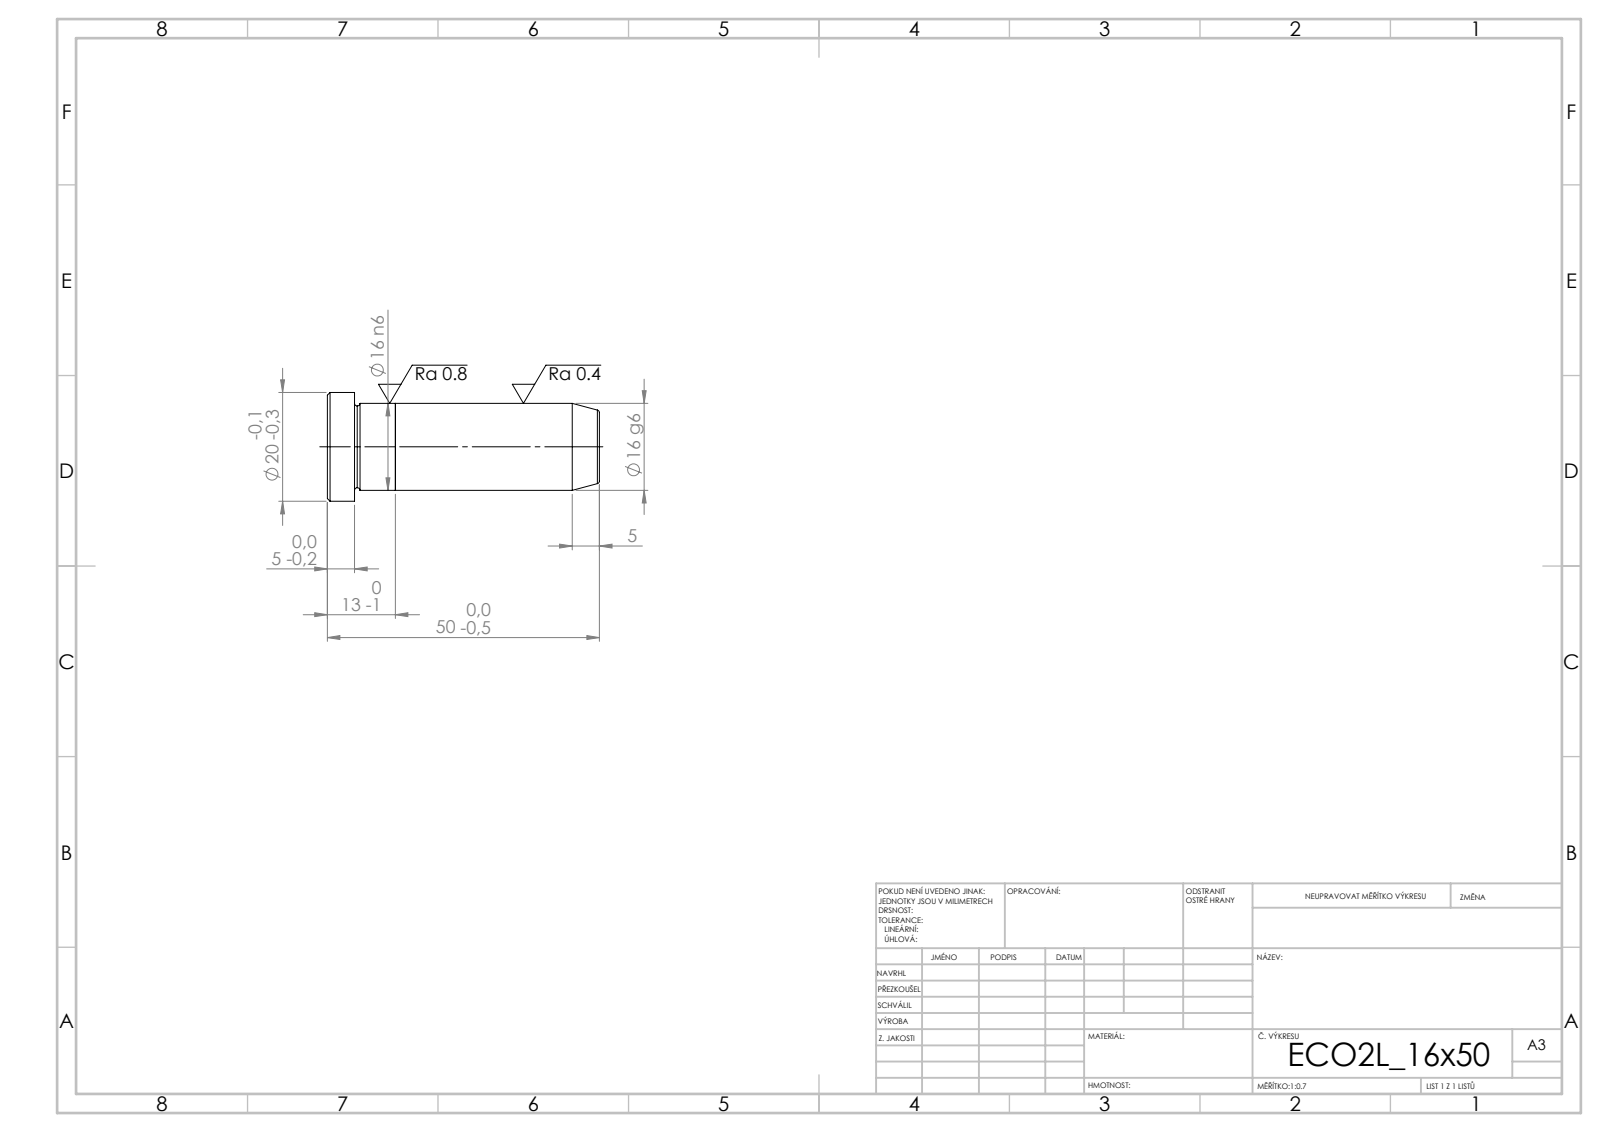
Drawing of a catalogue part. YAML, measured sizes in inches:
step_written_by: "SolidWorks 2019 (CONFIG_CONTROL_DESIGN)"
units: inches
bodies: {solids: 2, faces: 21, planar: 5, cylindrical: 6, other: 10}
overall_size: [1.969, 0.787, 0.787]
volume: 0.637
surface_area: 5.478
round_bosses_or_shafts:
  - {diameter: 0.787, count: 1}
  - {diameter: 0.63, count: 1}
face_to_face_distances: [0.492, 1.476, 1.969, 1.772, 0.295, 0.197]
